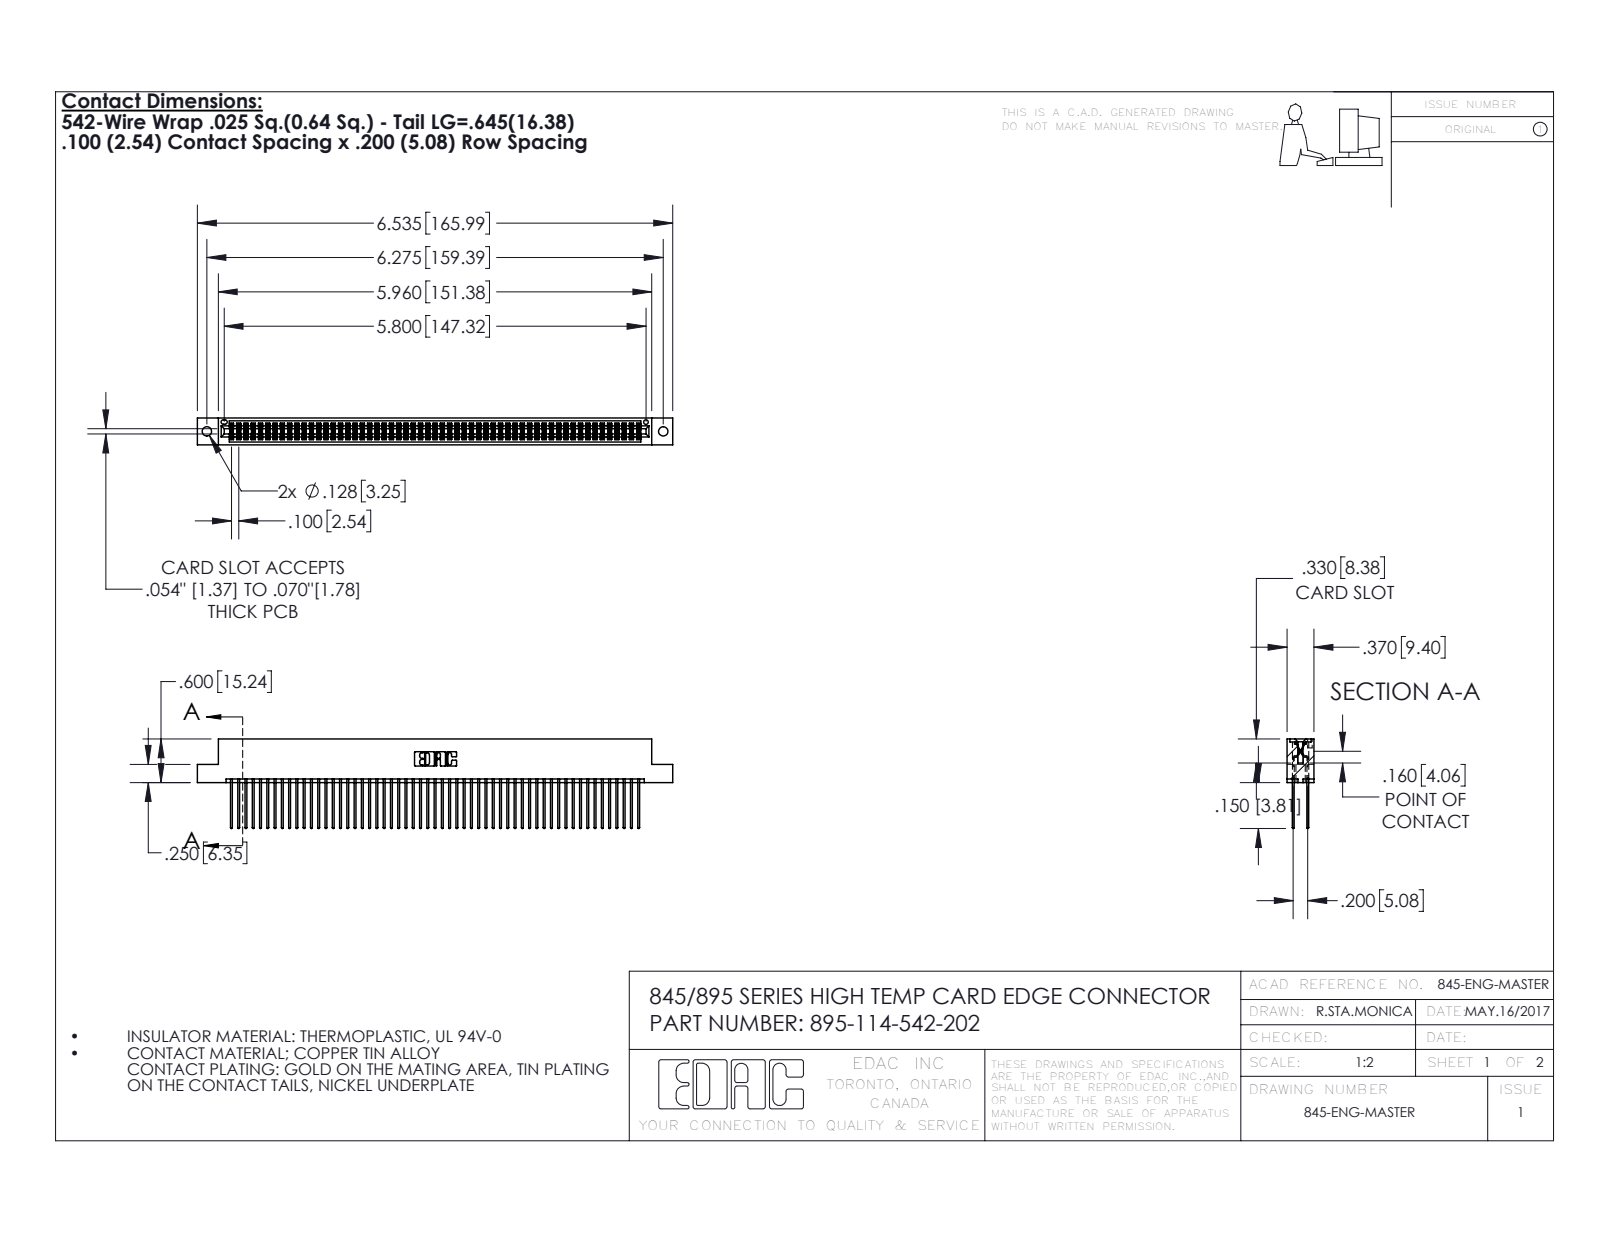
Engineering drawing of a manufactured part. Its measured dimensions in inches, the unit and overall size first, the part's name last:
Units: inches
Overall size (bounding box): 6.535 × 1.232 × 0.37
Round holes (diameter × count): ⌀0.128 ×2, ⌀0.064 ×1
Partial cylindrical surfaces — rounded edges, fillets, slot ends (radius × count): R0.006 ×172, R0.01 ×114, R0.01 ×22, R0.007 ×6, R0.031 ×6, R0.026 ×3, R0.014 ×2, R0.019 ×2
Main face-to-face distances: 0.298, 0.072, 0.2, 0.098, 0.272, 0.025, 0.225, 0.37, 0.175, 0.149
Hole centre spacings: 0.27, 6.039, 6.275
Volume: 1.023 in³ · Surface area: 42.27 in²
Bodies: 115 solids, 5826 faces (3842 planar, 1984 cylindrical, 0 other)
Part name (STEP PRODUCT): 345 Part_Flush Mounting Lugs - 0.128 Dia; 345-292-001_345-293-142; 395-114-542-202
STEP written by: SolidWorks 2016 (CONFIG_CONTROL_DESIGN)
